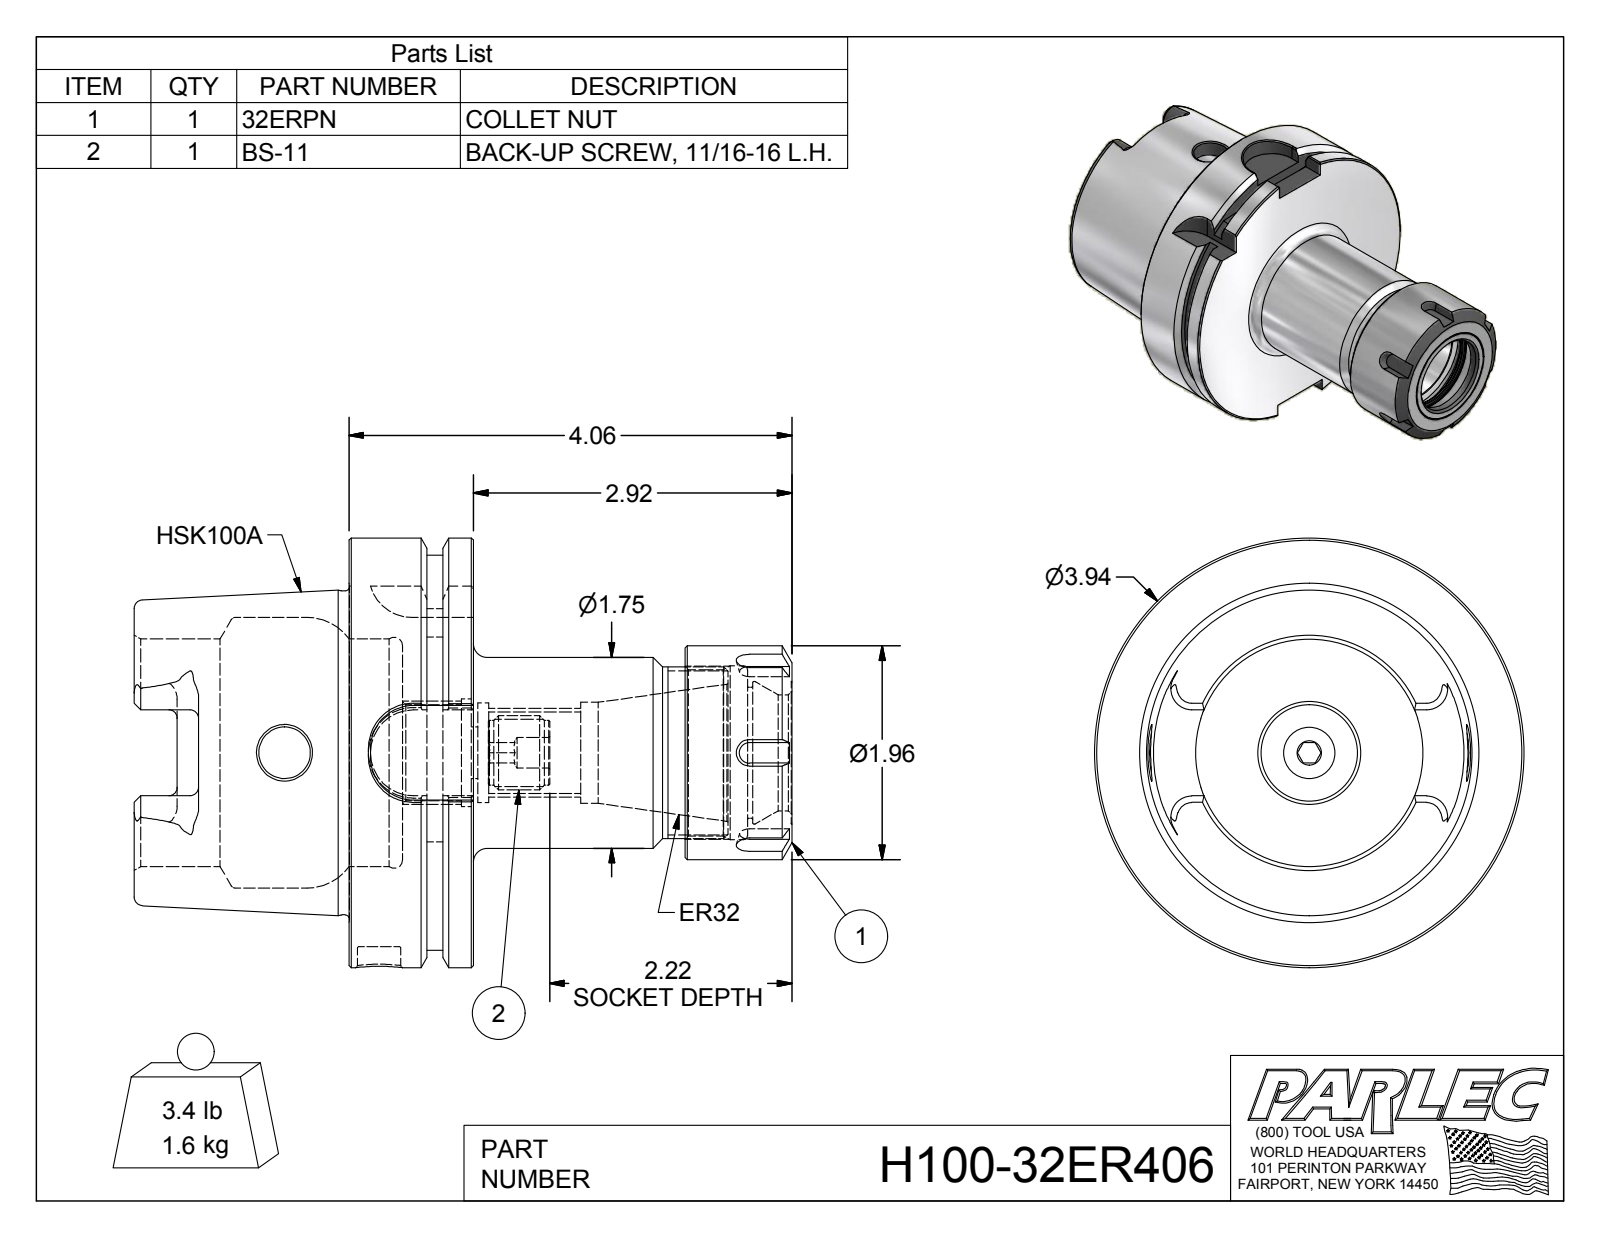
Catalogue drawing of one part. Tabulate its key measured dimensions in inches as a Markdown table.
| quantity | value |
| --- | --- |
| part name | H100-32ER406; H100-32ER4-1; 32ERPN; BS-11 |
| STEP written by | Autodesk Inventor 2012 (AUTOMOTIVE_DESIGN) |
| units | inches |
| bodies | 3 solids, 197 faces (76 planar, 46 cylindrical, 75 other) |
| overall size | 6.029 × 3.937 × 3.937 |
| volume | 20.64 in³ |
| surface area | 112.5 in² |
| round holes (diameter × count) | 0.472 × 2, 0.28 × 1, 0.394 × 1, 0.745 × 1, 0.881 × 1, 0.912 × 1, 0.925 × 1, 0.985 × 1, 1.063 × 1, 1.2 × 1, 1.305 × 1, 1.523 × 1 |
| round bosses / shafts (diameter × count) | 3.937 × 1, 2.967 × 1, 1.958 × 1, 1.75 × 1, 1.575 × 1, 0.681 × 1, 0.595 × 1 |
| partial cylindrical surfaces (radius × count) | 0.079 × 6, 0.192 × 4, 0.394 × 4, 1.811 × 1 |
| main face-to-face distances | 1.142, 0.492, 0.65, 3.11, 2.461, 1.969, 2.919, 3.568, 4.06, 6.029 |
